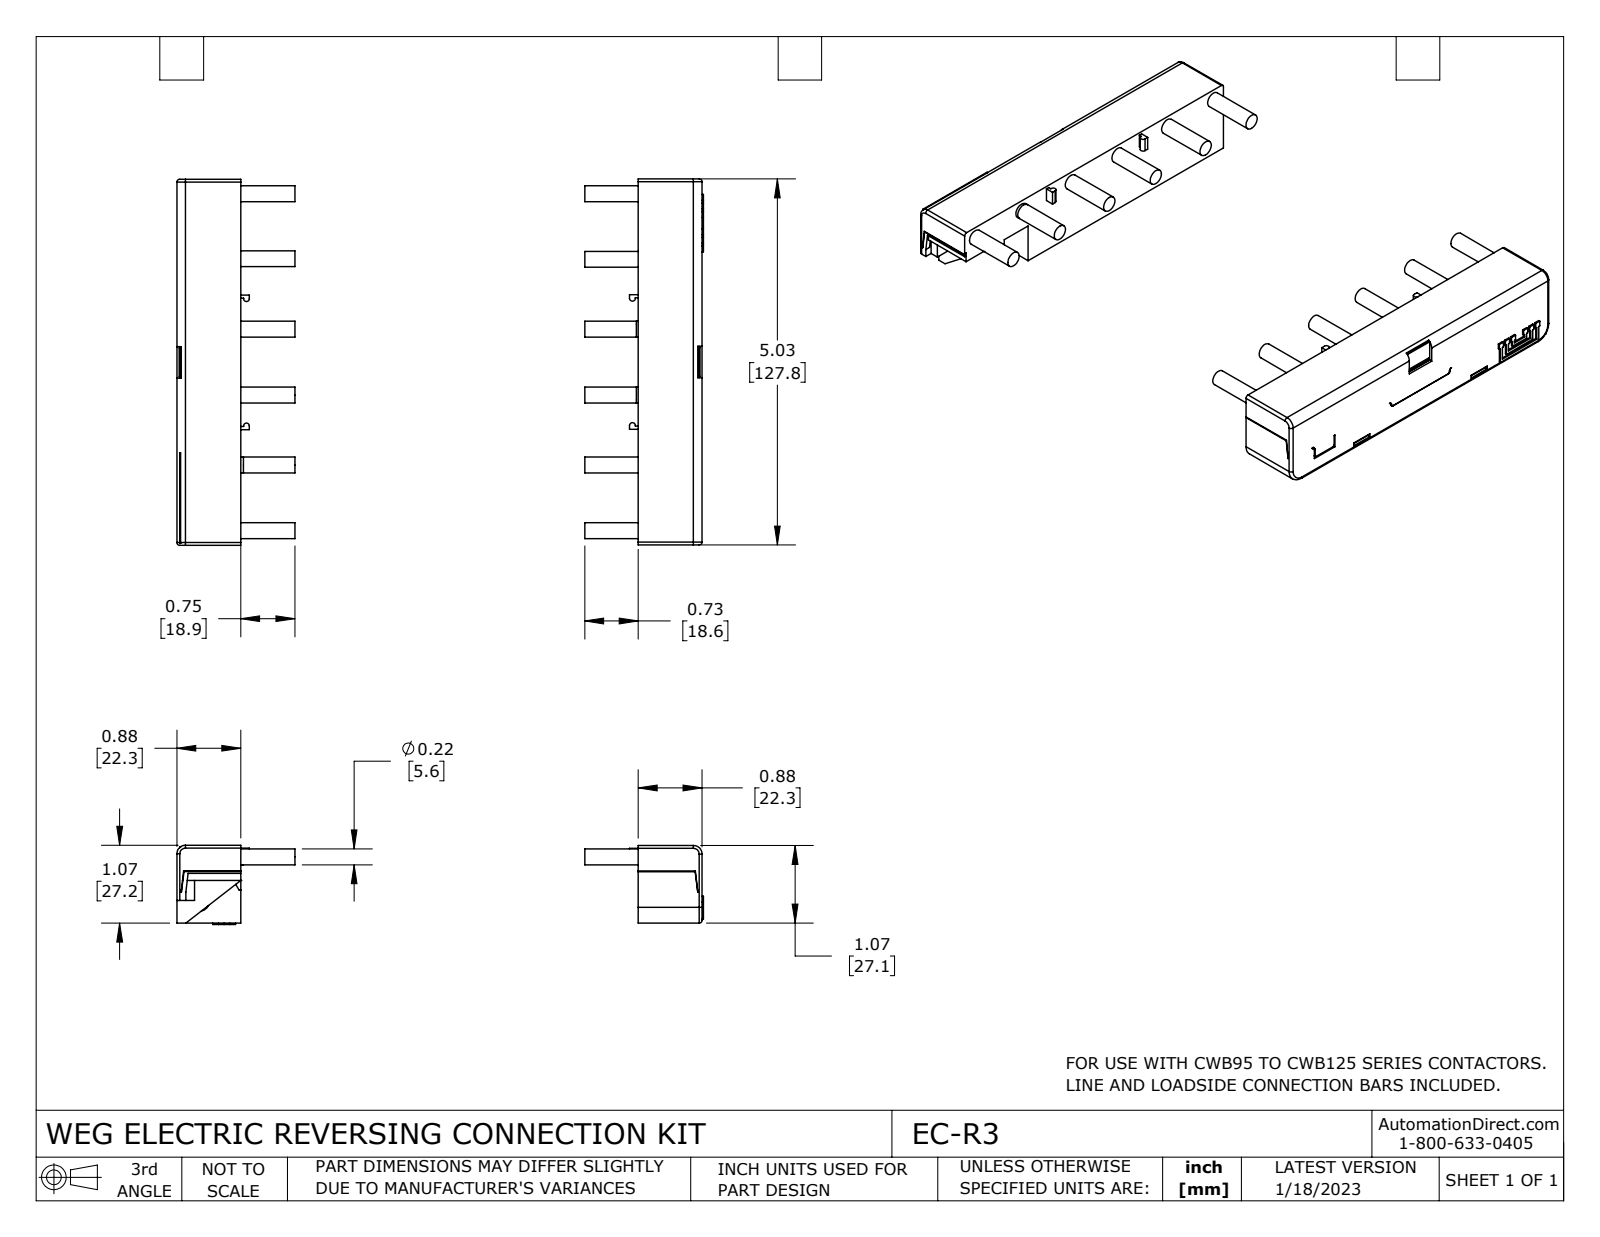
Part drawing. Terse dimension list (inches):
name: EC-R3
written by: SolidWorks 2021 (CONFIG_CONTROL_DESIGN)
unit: in
bodies: 2 solids, 399 faces (317 planar, 69 cylindrical, 13 other)
size: 7.24 × 5.037 × 1.091
volume: 9.347 in³; area: 50.06 in²
bosses: 7× ⌀0.219
rounds: 17× R0.039, 10× R0.02, 8× R0.035, 4× R0.031, 2× R0.118, 2× R0.217
face distances: 0.878, 6.343, 5.465, 7.22, 1.067, 1.07, 1.067, 1.071, 5.031, 5.026
